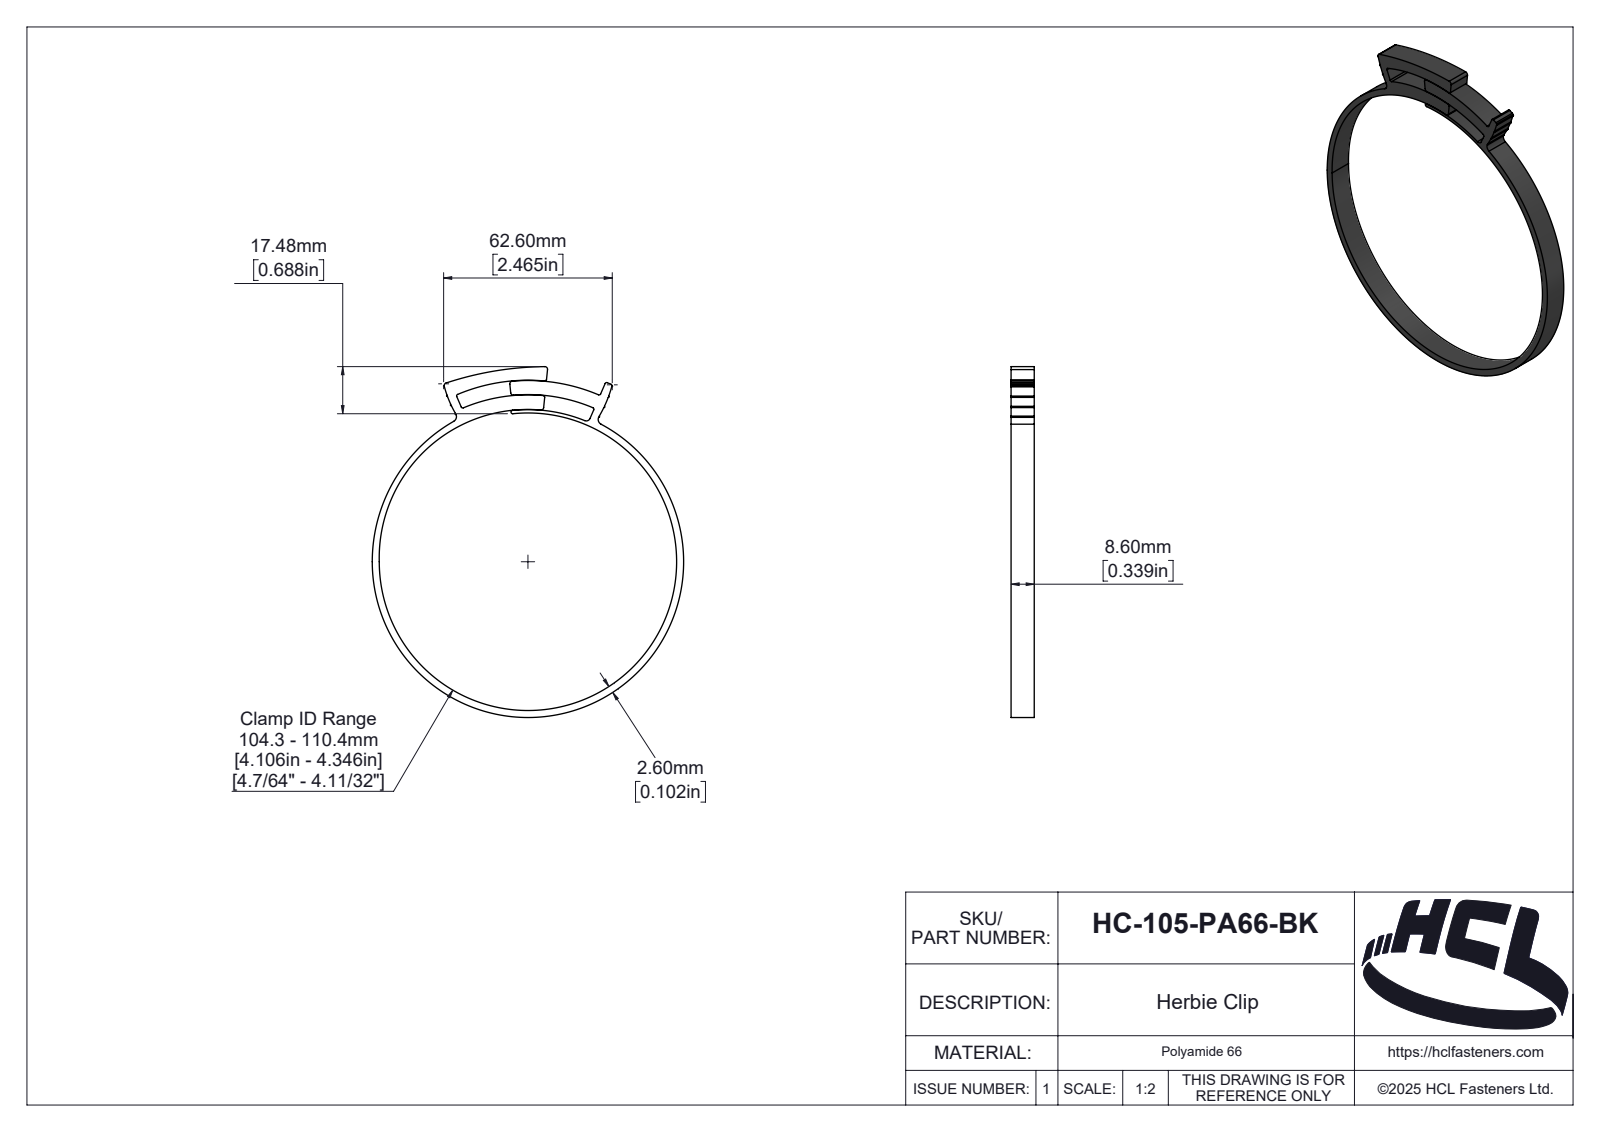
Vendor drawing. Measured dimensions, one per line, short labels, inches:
name: HC-105-PA66-BK
written by: SolidWorks 2025 (AUTOMOTIVE_DESIGN)
unit: in
bodies: 1 solid, 162 faces (13 planar, 100 cylindrical, 49 other)
size: 5.126 × 4.551 × 0.339
volume: 0.744 in³; area: 16.83 in²
rounds: 8× R0.01, 6× R0.024, 5× R0.039, 2× R0.079, 1× R0.007, 1× R0.024, 1× R0.026, 1× R0.033
face distances: 0.339
